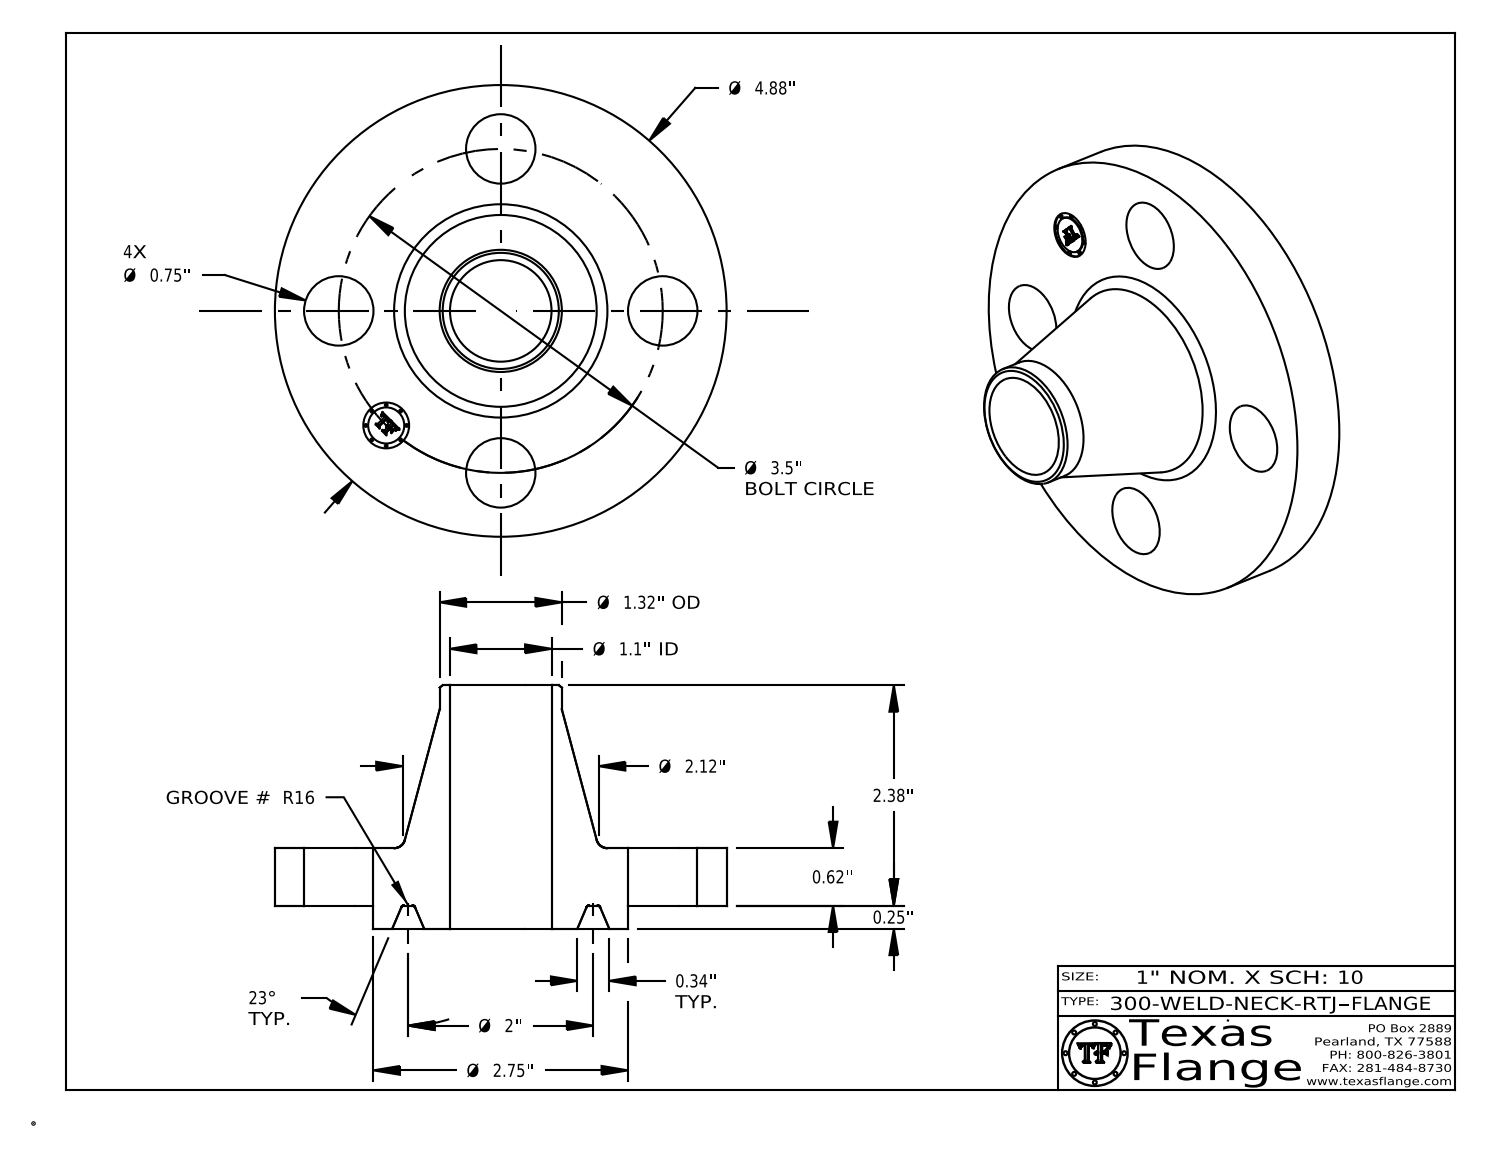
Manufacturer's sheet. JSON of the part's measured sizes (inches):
{"part_name": "300-WELD-NECK-RTJ", "step_written_by": "CATIA V5 STEP AP214 (AUTOMOTIVE_DESIGN)", "units": "inches", "bodies": {"solids": 1, "faces": 421, "planar": 371, "cylindrical": 36, "other": 14}, "overall_size": [4.88, 4.88, 2.63], "volume_in3": 13.04, "surface_area_in2": 67.73, "round_holes": [[0.75, 4], [0.495, 1], [1.097, 1]], "round_bosses_or_shafts": [[0.03, 8], [4.88, 1], [2.75, 1], [1.32, 1], [0.39, 1]], "face_to_face_distances": [0.62, 0.25, 0.87, 2.63, 2.38, 1.76, 0.015, 0.855, 0.605, 1.775], "hole_center_spacings": [1.75, 2.475, 1.339, 3.233, 3.5]}
